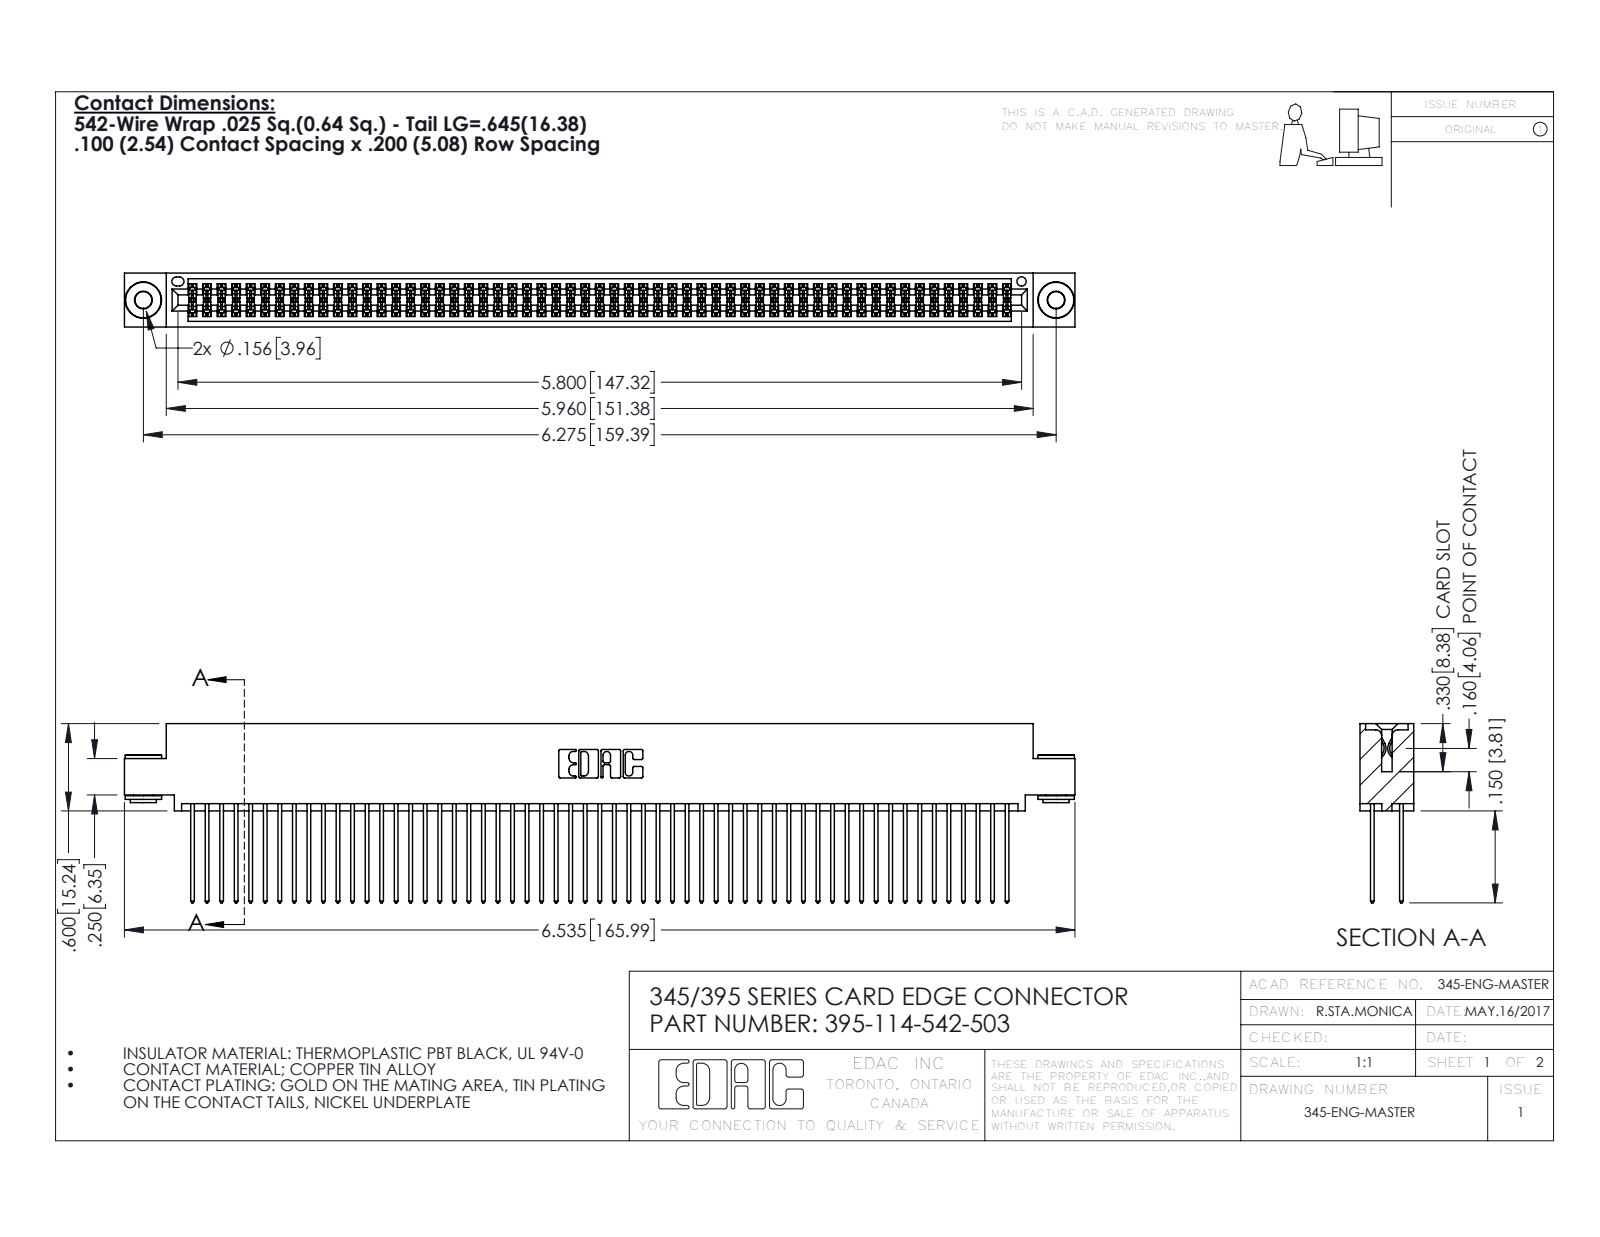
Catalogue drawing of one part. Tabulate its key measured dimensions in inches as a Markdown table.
| quantity | value |
| --- | --- |
| part name | 345-250-002_345-250-002-102; 345 Part_0.110 Offset - 0.156 Dia-TH; 395-114-542-503; 345-292-001_345-293-142 |
| STEP written by | SolidWorks 2016 (CONFIG_CONTROL_DESIGN) |
| units | inches |
| bodies | 117 solids, 5868 faces (3856 planar, 2004 cylindrical, 8 other) |
| overall size | 6.535 × 1.232 × 0.37 |
| volume | 1.022 in³ |
| surface area | 43.12 in² |
| round holes (diameter × count) | 0.116 × 2, 0.156 × 2, 0.064 × 1 |
| round bosses / shafts (diameter × count) | 0.25 × 2, 0.18 × 2, 0.136 × 2 |
| partial cylindrical surfaces (radius × count) | 0.006 × 171, 0.01 × 114, 0.01 × 22, 0.007 × 6, 0.031 × 6, 0.026 × 3, 0.014 × 2, 0.019 × 2 |
| main face-to-face distances | 0.072, 0.298, 0.2, 0.025, 0.098, 0.272, 0.225, 0.37, 0.175, 0.149 |
| hole center spacings | 0.27, 6.039, 6.275 |
